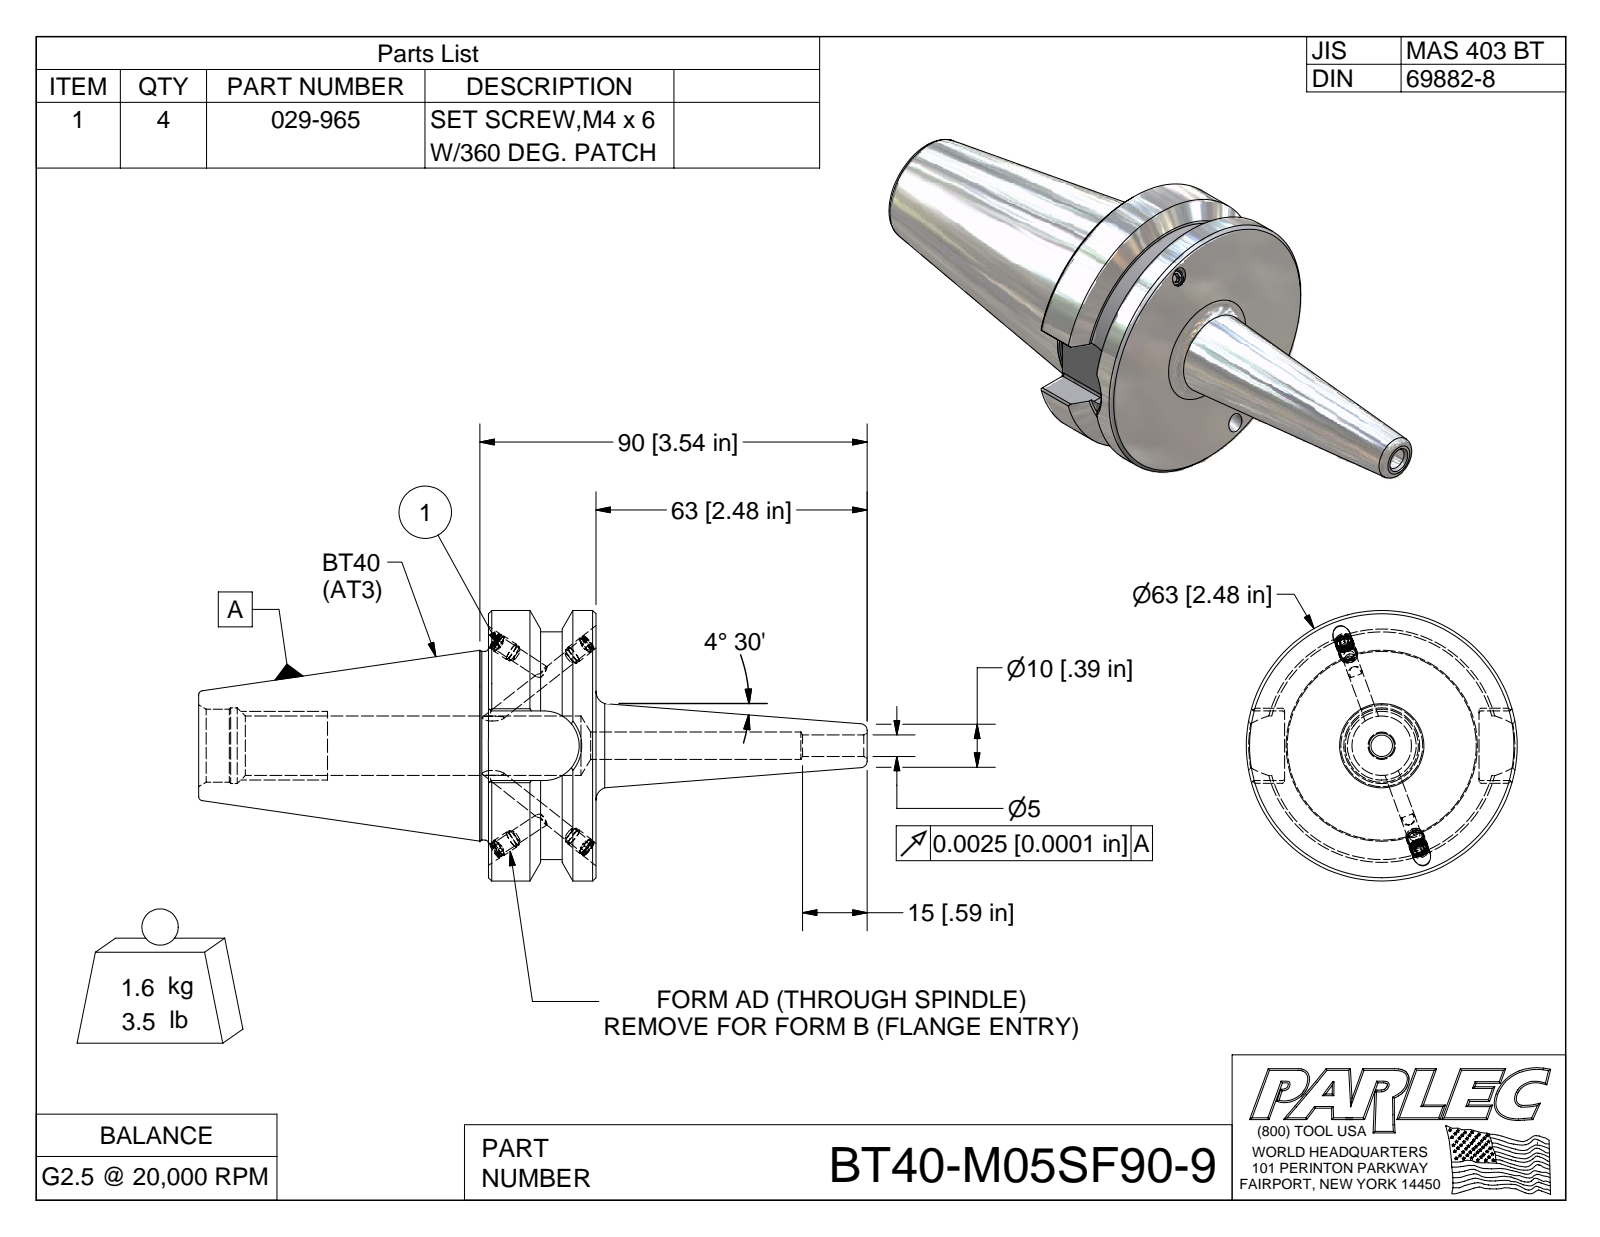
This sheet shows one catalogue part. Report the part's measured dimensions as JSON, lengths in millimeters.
{"part_name": "BT40-M05SF90-9; BT40BC-M05SF90-9-1; 029-965", "step_written_by": "Autodesk Inventor 2009 (AUTOMOTIVE_DESIGN)", "units": "millimeters", "bodies": {"solids": 5, "faces": 149, "planar": 67, "cylindrical": 39, "other": 43}, "overall_size": [155.4, 63, 63], "volume_mm3": 128900, "surface_area_mm2": 27610, "round_holes": [[3.3, 4], [4.1, 4], [5, 1], [17.6, 1]], "round_bosses_or_shafts": [[4.2, 4], [4, 4], [63, 1], [53, 1], [44.5, 1], [43.9, 1]], "partial_cylinders_radius": [[0.5, 8], [8.1, 1]], "face_to_face_distances": [25, 45.2, 67.4, 92.4, 16.2, 84.5, 17.1, 7.8, 79.5, 12.1]}
